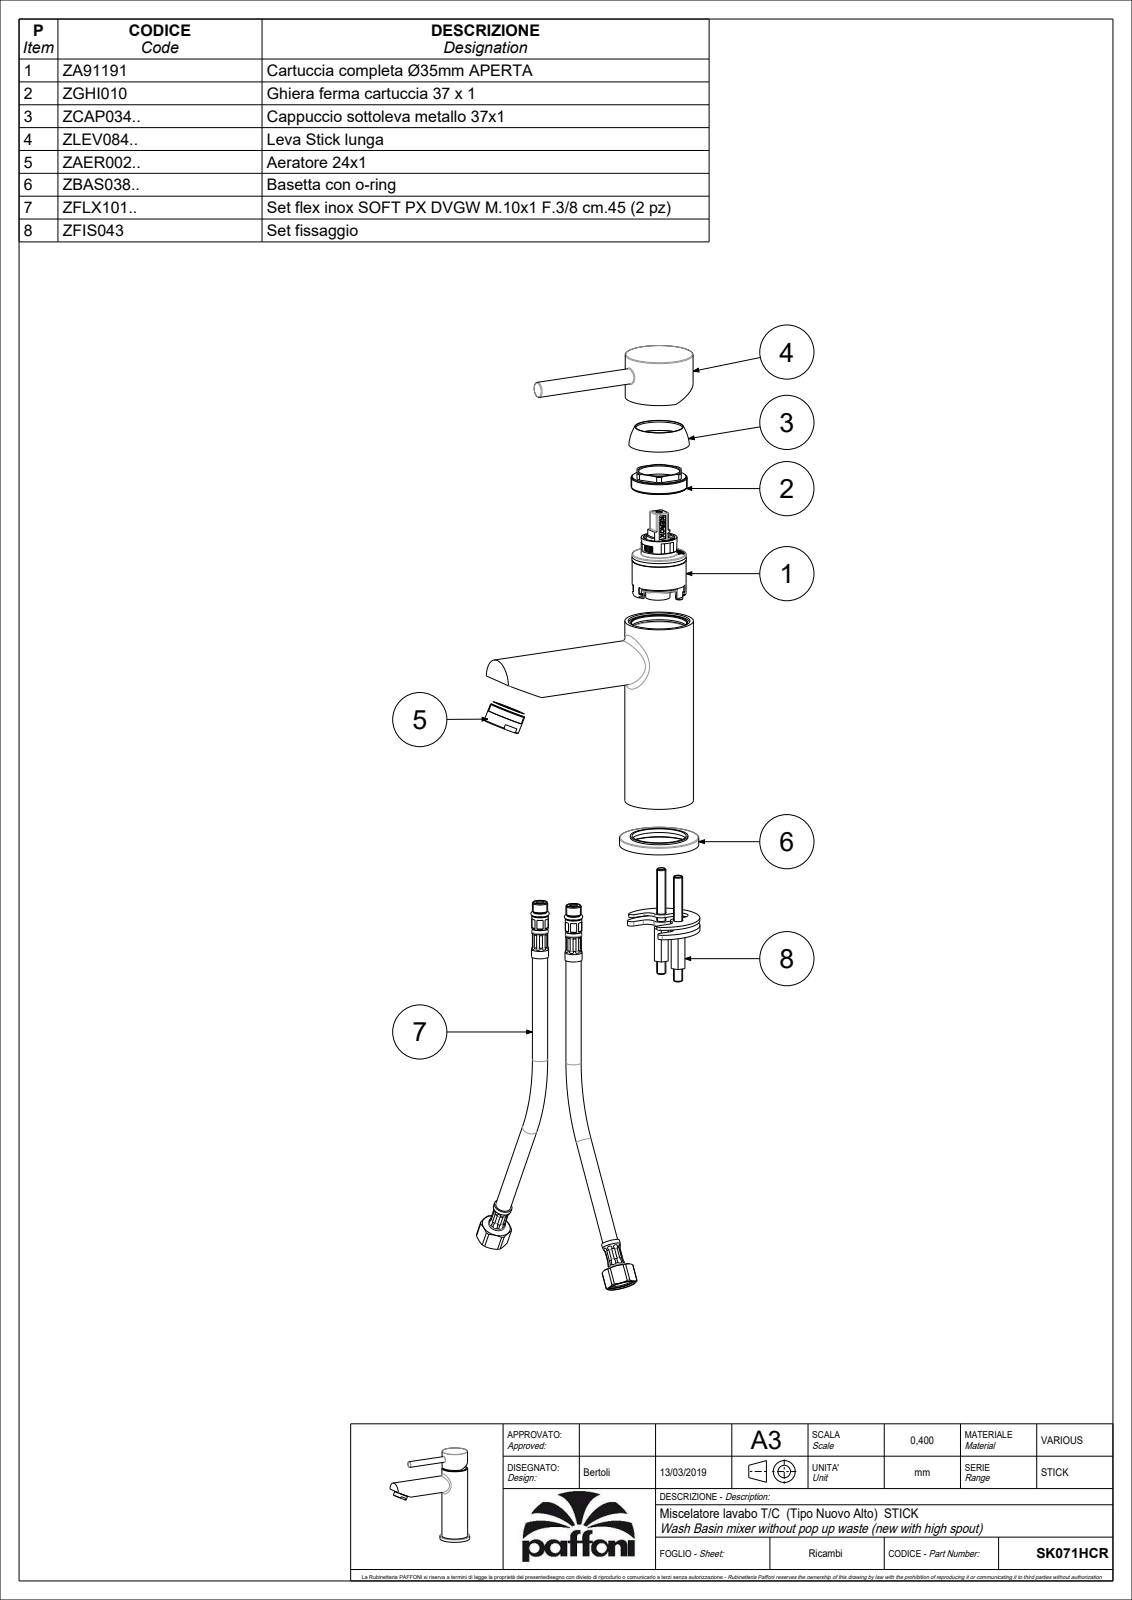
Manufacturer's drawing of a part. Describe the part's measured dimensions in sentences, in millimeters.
The part is named "SK071HCR". Its 3-D file was written by "CREO PARAMETRIC BY PTC INC, 2020044 (CONFIG_CONTROL_DESIGN)". It is 3 solids with 3223 faces: 2356 planar, 465 cylindrical and 402 other. Overall it measures 158.64 by 148.5 by 52 millimeters. Its volume is 141 591 cubic millimeters and its surface area 92 421 square millimeters. Round holes: 2 of diameter 5, 2 of diameter 5.5, 2 of diameter 7, 2 of diameter 8, 2 of diameter 9, 2 of diameter 11, 1 of diameter 3, 1 of diameter 3.4, 1 of diameter 3.5, 1 of diameter 4, 1 of diameter 4.6, 1 of diameter 5.6. Round bosses or shafts: 2 of diameter 14, 2 of diameter 9, 2 of diameter 4.8, 1 of diameter 52, 1 of diameter 45, 1 of diameter 44.5, 1 of diameter 42.6, 1 of diameter 37.8. Partial cylindrical surfaces (rounded edges, fillets, slot ends): 58 of radius 0.5, 18 of radius 1, 9 of radius 1.5, 6 of radius 1.7, 4 of radius 0.8, 4 of radius 5.8, 3 of radius 12.75, 2 of radius 0.3. The main face-to-face distances are 1, 0.5, 9.5, 47.65, 15.85, 63.5, 5, 3.2, 1.5, 125.2. The hole center spacings are 13.6, 2, 2.83, 8.6, 10.3, 13.15, 13.45, 15.
